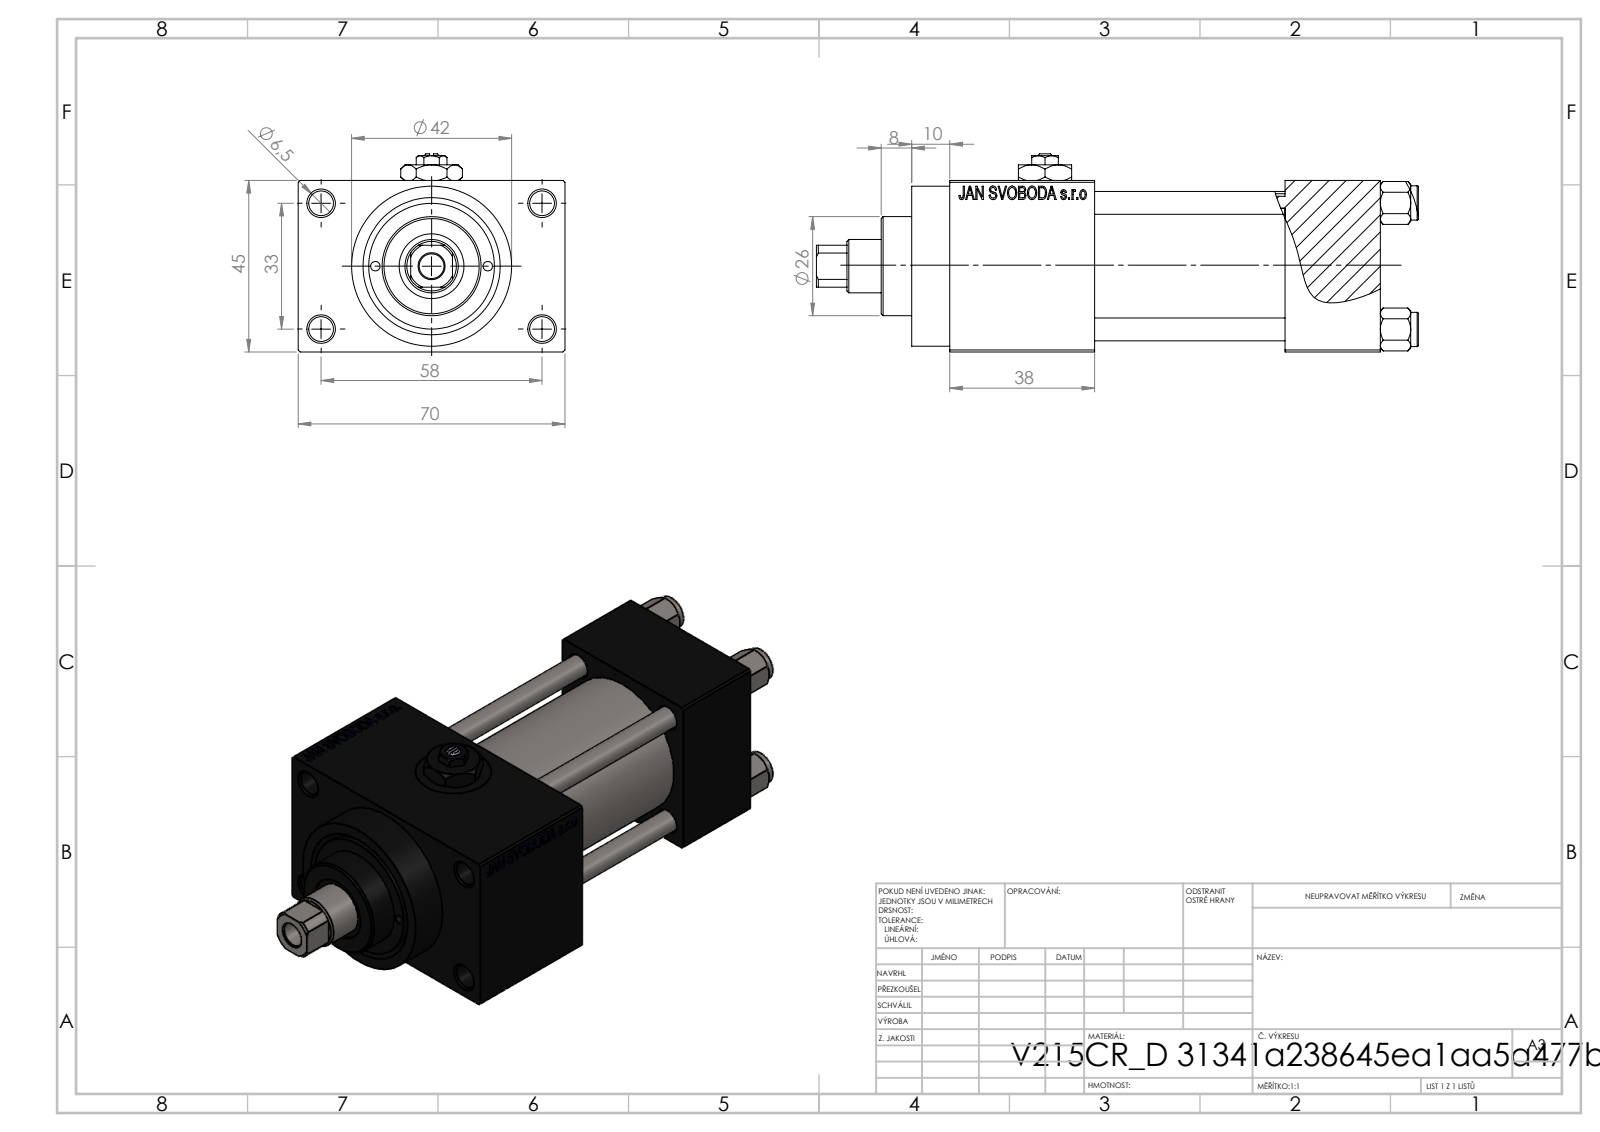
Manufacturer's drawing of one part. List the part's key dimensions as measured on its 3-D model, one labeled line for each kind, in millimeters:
Part name (STEP PRODUCT): V215_VC_A; V215CR_D_TYCINKA; V215CR_VCP_D; NUT_M5_D (+2 more)
STEP written by: SolidWorks 2019 (CONFIG_CONTROL_DESIGN)
Units: millimetres
Bodies: 12 solids, 1157 faces (521 planar, 96 cylindrical, 540 other)
Overall size (bounding box): 158 × 70 × 52
Volume: 230 080 mm³ · Surface area: 75 980 mm²
Round holes (diameter × count): ⌀6.5 ×5, ⌀6 ×4, ⌀13.16 ×3, ⌀20 ×3, ⌀2.5 ×2, ⌀7 ×2, ⌀14 ×1, ⌀17 ×1, ⌀24 ×1, ⌀32 ×1, ⌀33 ×1
Round bosses / shafts (diameter × count): ⌀9 ×4, ⌀42 ×1, ⌀38 ×1, ⌀26 ×1
Partial cylindrical surfaces — rounded edges, fillets, slot ends (radius × count): R6.5 ×1
Main face-to-face distances: 45, 25, 50, 12.5, 75, 57.5, 88, 38, 113, 70
Hole centre spacings: 12.4, 16.7, 21.8, 23.48, 33.2, 33.37, 35.35, 35.47
